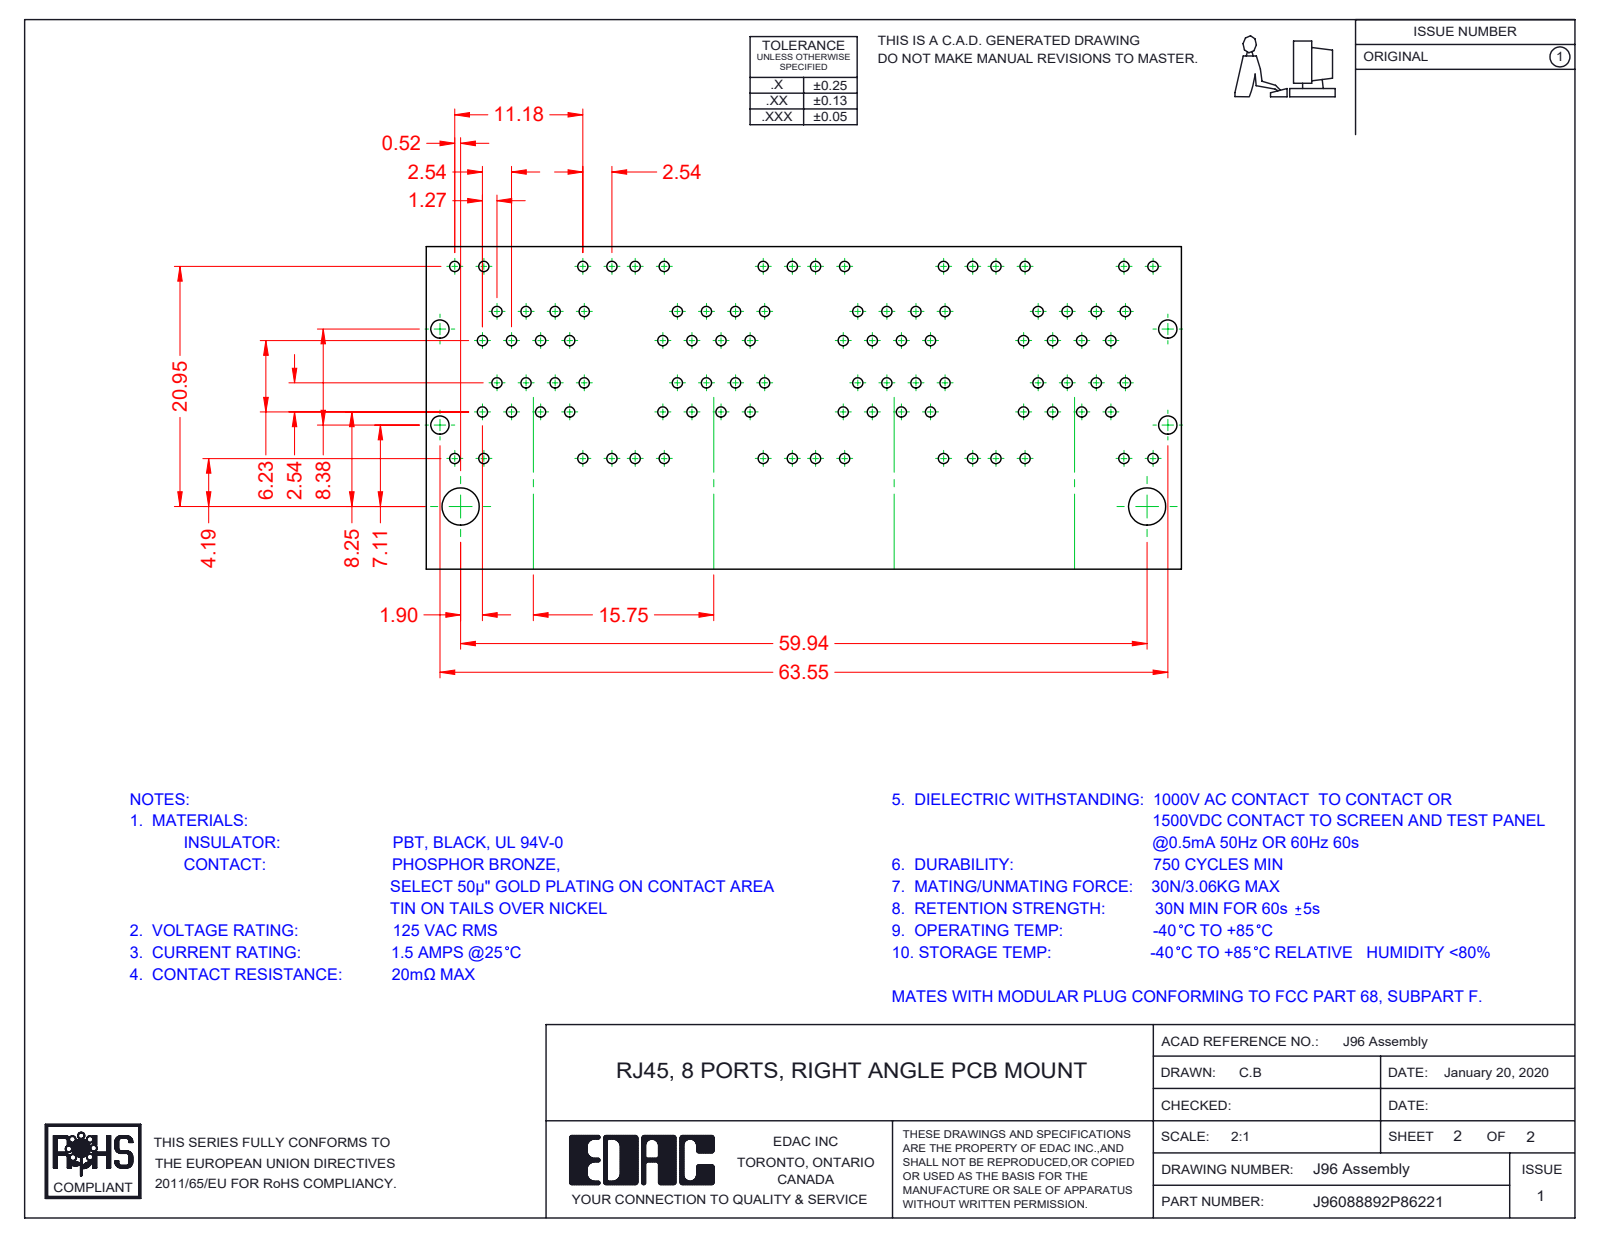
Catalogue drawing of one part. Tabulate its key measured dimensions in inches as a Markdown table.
| quantity | value |
| --- | --- |
| part name | 96 LED LH Upper_8-Red-Yellow; 96 Contacts Lower; 96 Insulator Insert; 96 Contacts Upper (+8 more) |
| STEP written by | SolidWorks 2016 (CONFIG_CONTROL_DESIGN) |
| units | inches |
| bodies | 96 solids, 7836 faces (6105 planar, 1420 cylindrical, 311 other) |
| overall size | 2.652 × 1.235 × 1.129 |
| volume | 1.474 in³ |
| surface area | 98.57 in² |
| round holes (diameter × count) | 0.067 × 3 |
| round bosses / shafts (diameter × count) | 0.066 × 3 |
| partial cylindrical surfaces (radius × count) | 0.01 × 124, 0.014 × 73, 0.039 × 72, 0.02 × 49, 0.036 × 32, 0.008 × 27, 0.011 × 14, 0.028 × 11 |
| main face-to-face distances | 0.62, 0.014, 0.392, 0.046, 0.063, 0.021, 0.393, 0.401, 0.499, 0.133 |
| hole center spacings | 0.62, 1.24 |
